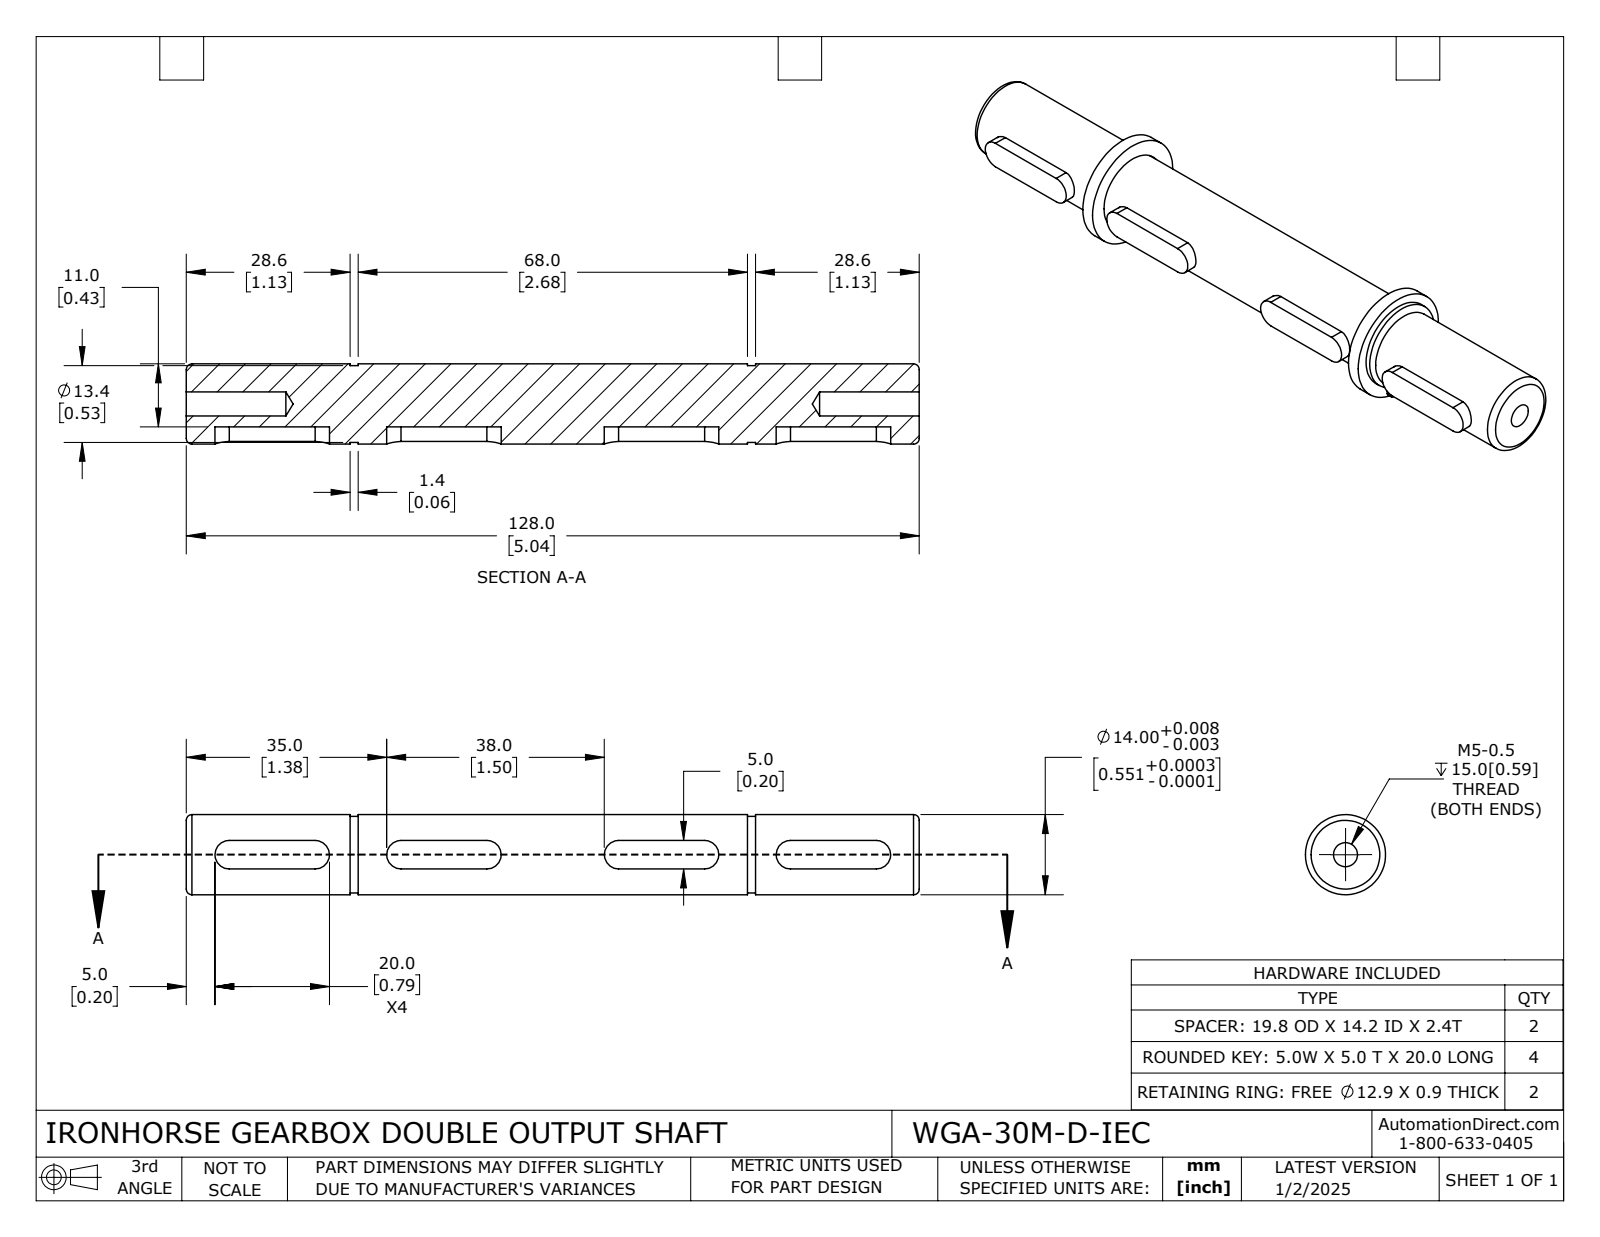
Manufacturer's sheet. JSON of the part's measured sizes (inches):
{"part_name": "WGA-30M-D-IEC", "step_written_by": "SolidWorks 2024 (CONFIG_CONTROL_DESIGN)", "units": "inches", "bodies": {"solids": 9, "faces": 136, "planar": 54, "cylindrical": 74, "other": 8}, "overall_size": [5.039, 0.78, 0.78], "volume_in3": 1.27, "surface_area_in2": 15.7, "round_holes": [[0.047, 2], [0.165, 1], [0.522, 1], [0.559, 1]], "round_bosses_or_shafts": [[0.78, 1], [0.626, 1], [0.551, 1], [0.528, 1]], "partial_cylinders_radius": [[0.098, 8], [0.02, 2], [0.071, 2]], "face_to_face_distances": [0.197, 0.094, 2.583, 2.677, 1.181, 1.276, 3.764, 3.858, 2.488, 1.146], "hole_center_spacings": [0.324, 0.083]}
